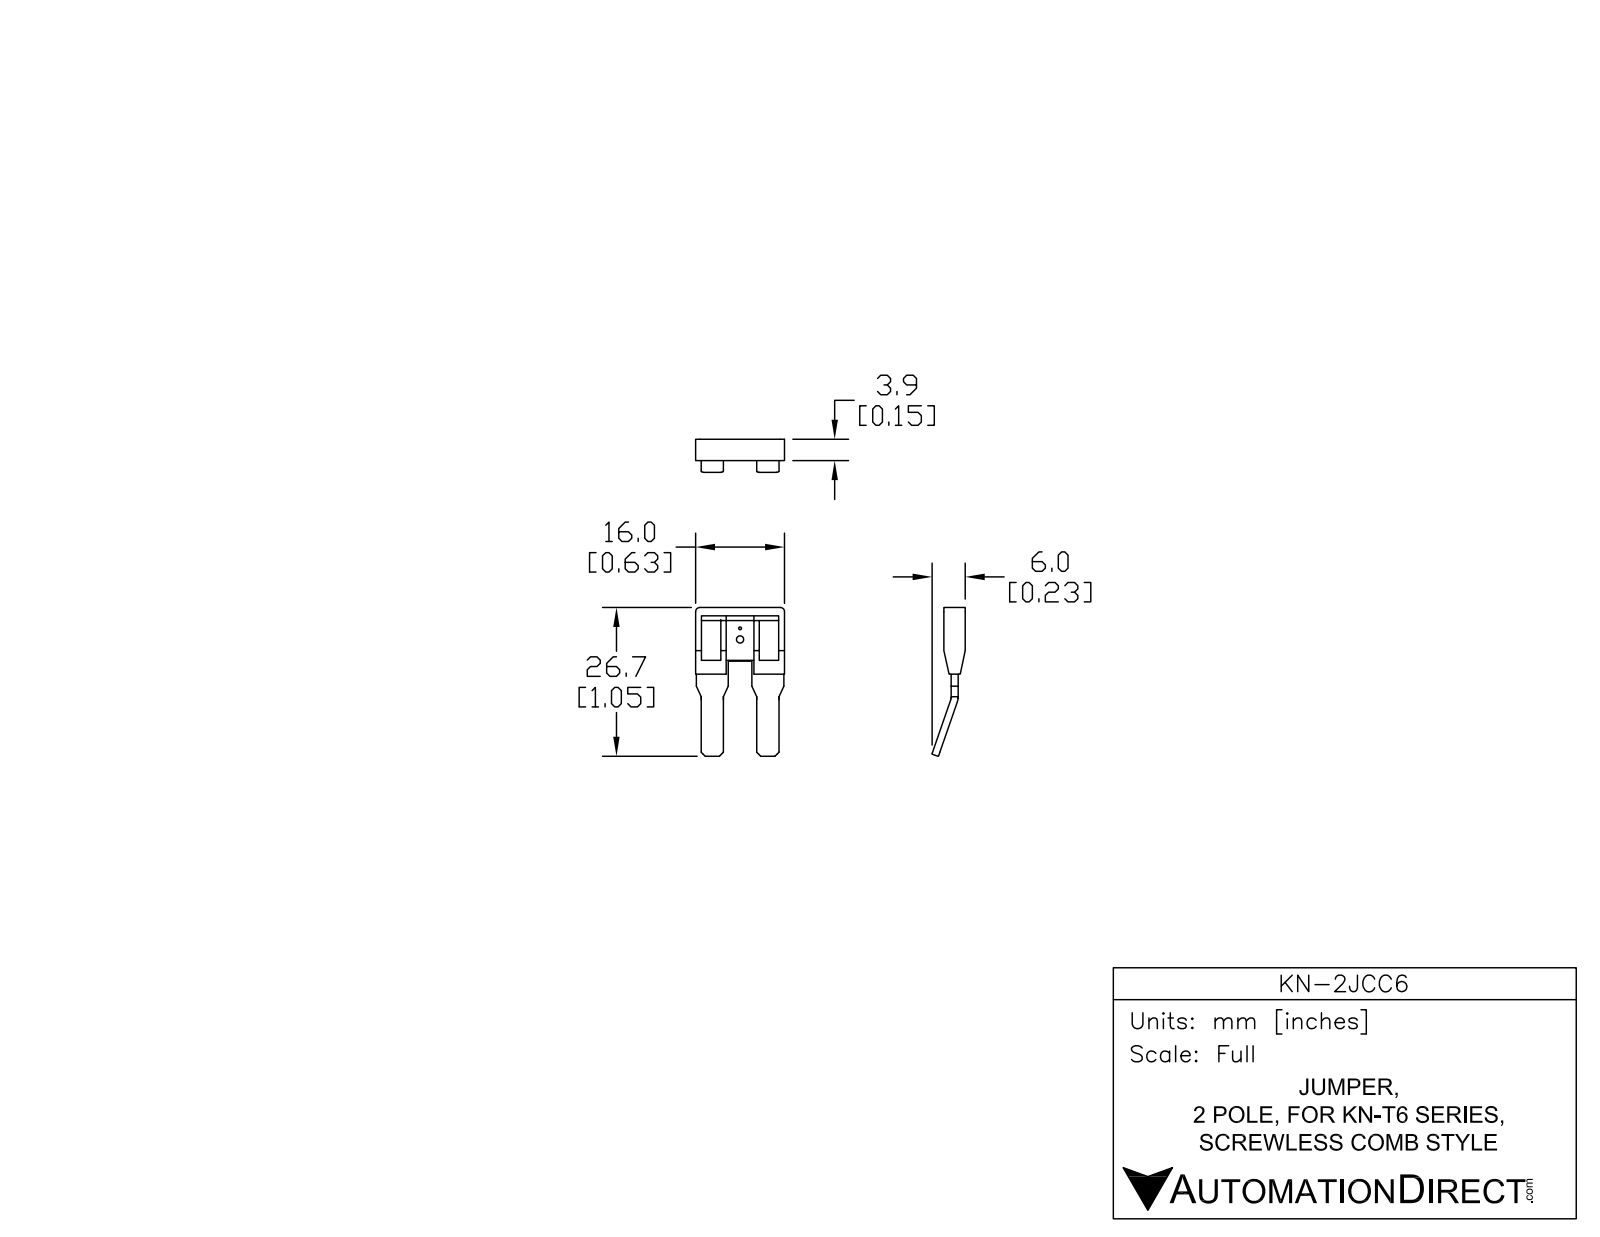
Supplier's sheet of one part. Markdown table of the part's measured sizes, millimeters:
| quantity | value |
| --- | --- |
| part name | KN-2JCC6 |
| STEP written by | SolidWorks 2014 (AUTOMOTIVE_DESIGN) |
| units | millimeters |
| bodies | 1 solid, 140 faces (72 planar, 41 cylindrical, 27 other) |
| overall size | 26.75 × 16 × 5.97 |
| volume | 703 mm³ |
| surface area | 1 009 mm² |
| round holes (diameter × count) | 0.5 × 1, 1.3 × 1 |
| partial cylindrical surfaces (radius × count) | 0.12 × 25, 0.5 × 2, 0.75 × 2, 1.29 × 1, 2.54 × 1 |
| main face-to-face distances | 1.25, 3, 0.85, 1.33, 3.43, 0.43, 0.42, 3.42, 3.85, 2.52 |
| hole center spacings | 2 |
